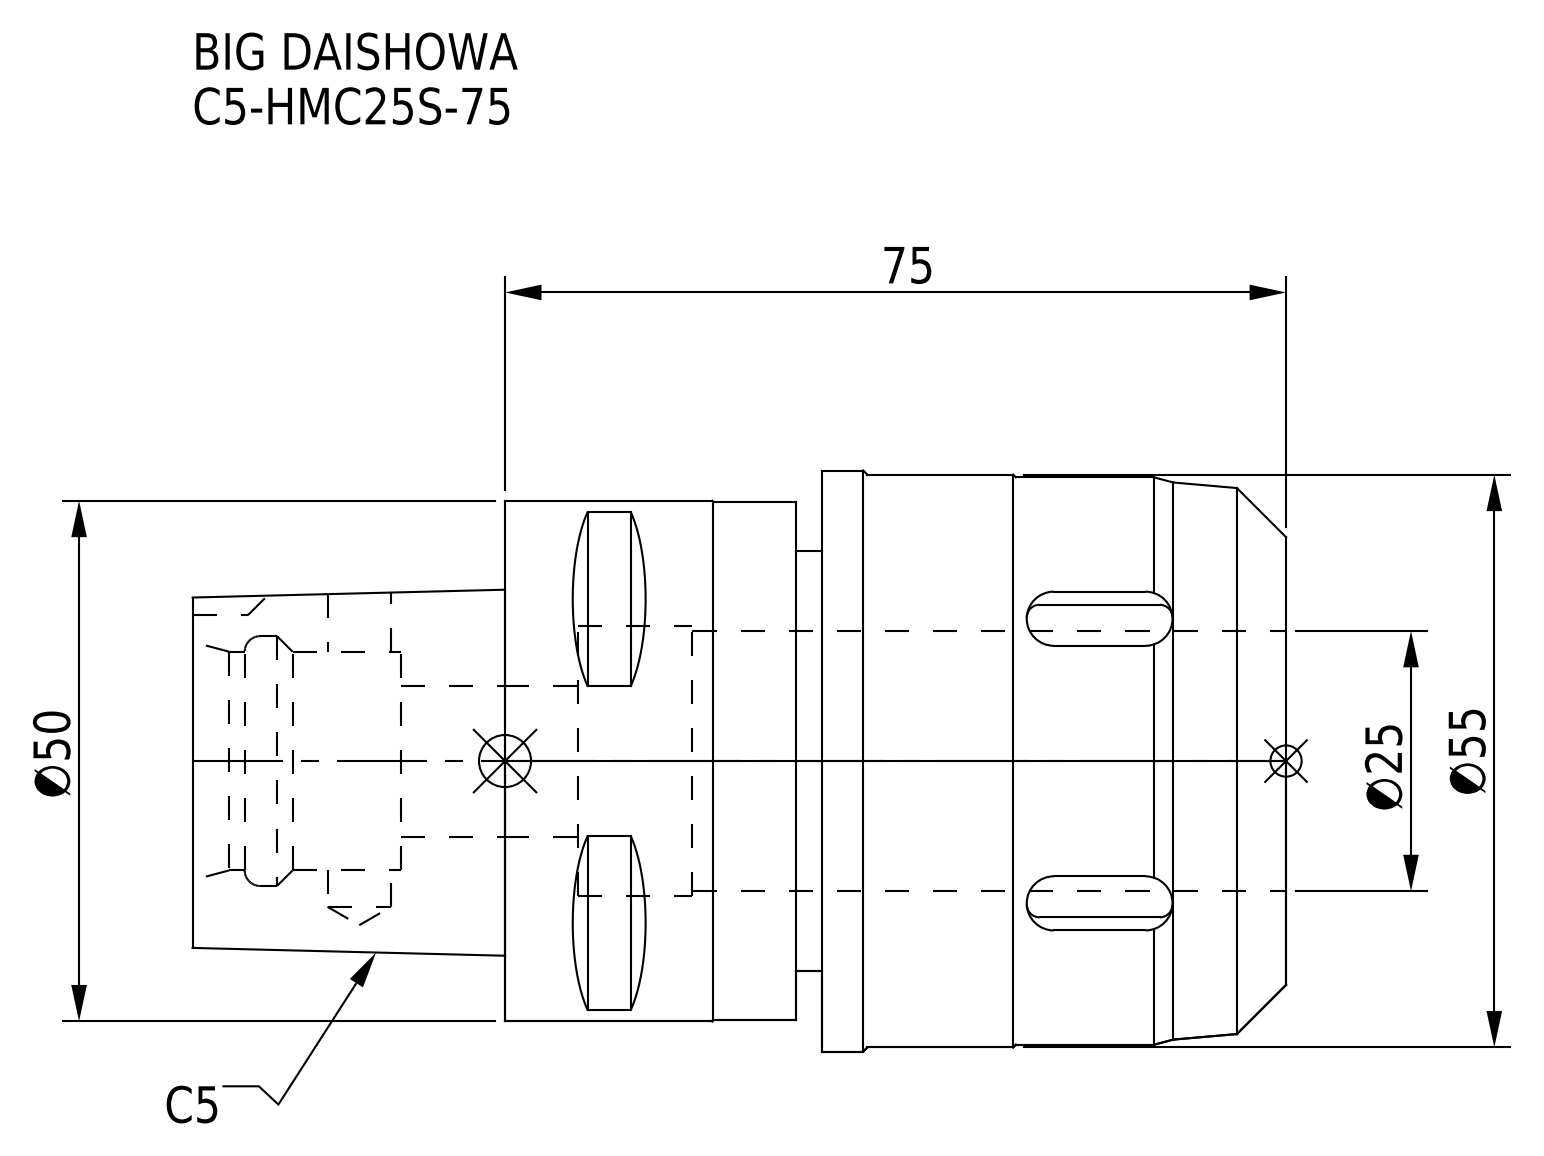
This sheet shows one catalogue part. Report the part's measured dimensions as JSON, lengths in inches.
{"part_name": "C5-HMC25S-75", "step_written_by": "CREO PARAMETRIC BY PTC INC, 2016380 (AUTOMOTIVE_DESIGN)", "units": "inches", "bodies": {"solids": 1, "faces": 111, "planar": 48, "cylindrical": 41, "other": 22}, "overall_size": [4.134, 2.197, 2.197], "volume_in3": 8.592, "surface_area_in2": 45.09, "round_holes": [[0.24, 1], [0.571, 1], [0.827, 1], [0.945, 1], [0.984, 1], [1.024, 1]], "round_bosses_or_shafts": [[2.197, 1], [2.165, 1], [2.146, 1], [1.969, 1], [1.961, 1], [1.587, 1]], "partial_cylinders_radius": [[0.118, 6], [0.157, 1]], "face_to_face_distances": [1.197, 1.756, 2.953, 1.854, 0.098, 1.098, 4.134, 2.378, 2.28, 1.181]}
